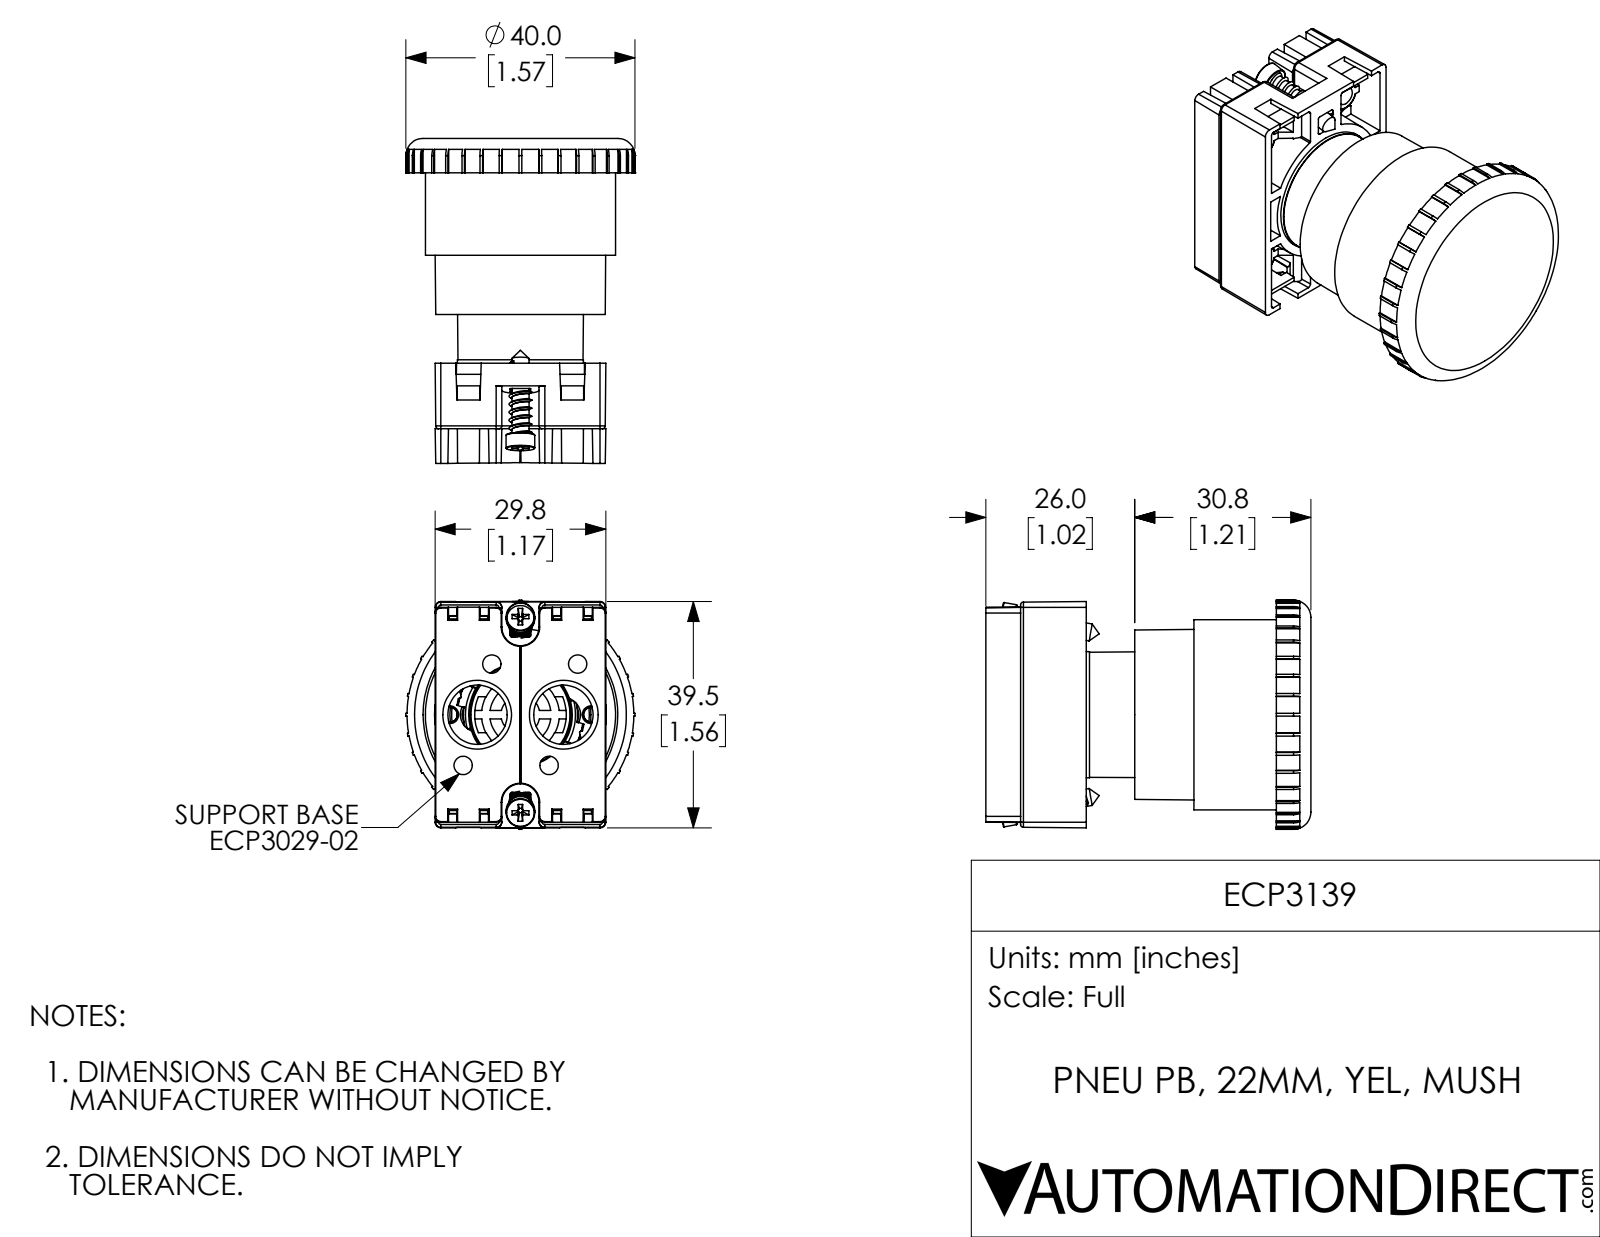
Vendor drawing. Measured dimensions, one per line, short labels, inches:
name: ECP3139
written by: SolidWorks 2017 (AUTOMOTIVE_DESIGN)
unit: in
bodies: 7 solids, 993 faces (478 planar, 233 cylindrical, 282 other)
size: 2.234 × 1.575 × 1.575
volume: 1.199 in³; area: 39.12 in²
holes: 4× ⌀0.081, 2× ⌀0.407, 1× ⌀0.102, 1× ⌀0.421, 1× ⌀0.697, 1× ⌀0.748, 1× ⌀0.756, 1× ⌀1.181, 1× ⌀1.457
bosses: 2× ⌀0.197, 2× ⌀0.118, 1× ⌀1.559, 1× ⌀1.307, 1× ⌀0.886, 1× ⌀0.866, 1× ⌀0.535
rounds: 18× R0.02, 8× R0.006, 8× R0.012, 4× R0.008, 4× R0.039, 2× R0.008, 2× R0.118, 2× R0.128
face distances: 1.995, 0.059, 1.936, 0.177, 0.067, 0.715, 1.544, 1.485, 0.451, 0.587
hole spacings: 0.304, 0.541, 0.817, 0.295, 0.472, 0.972, 1.081, 0.591
